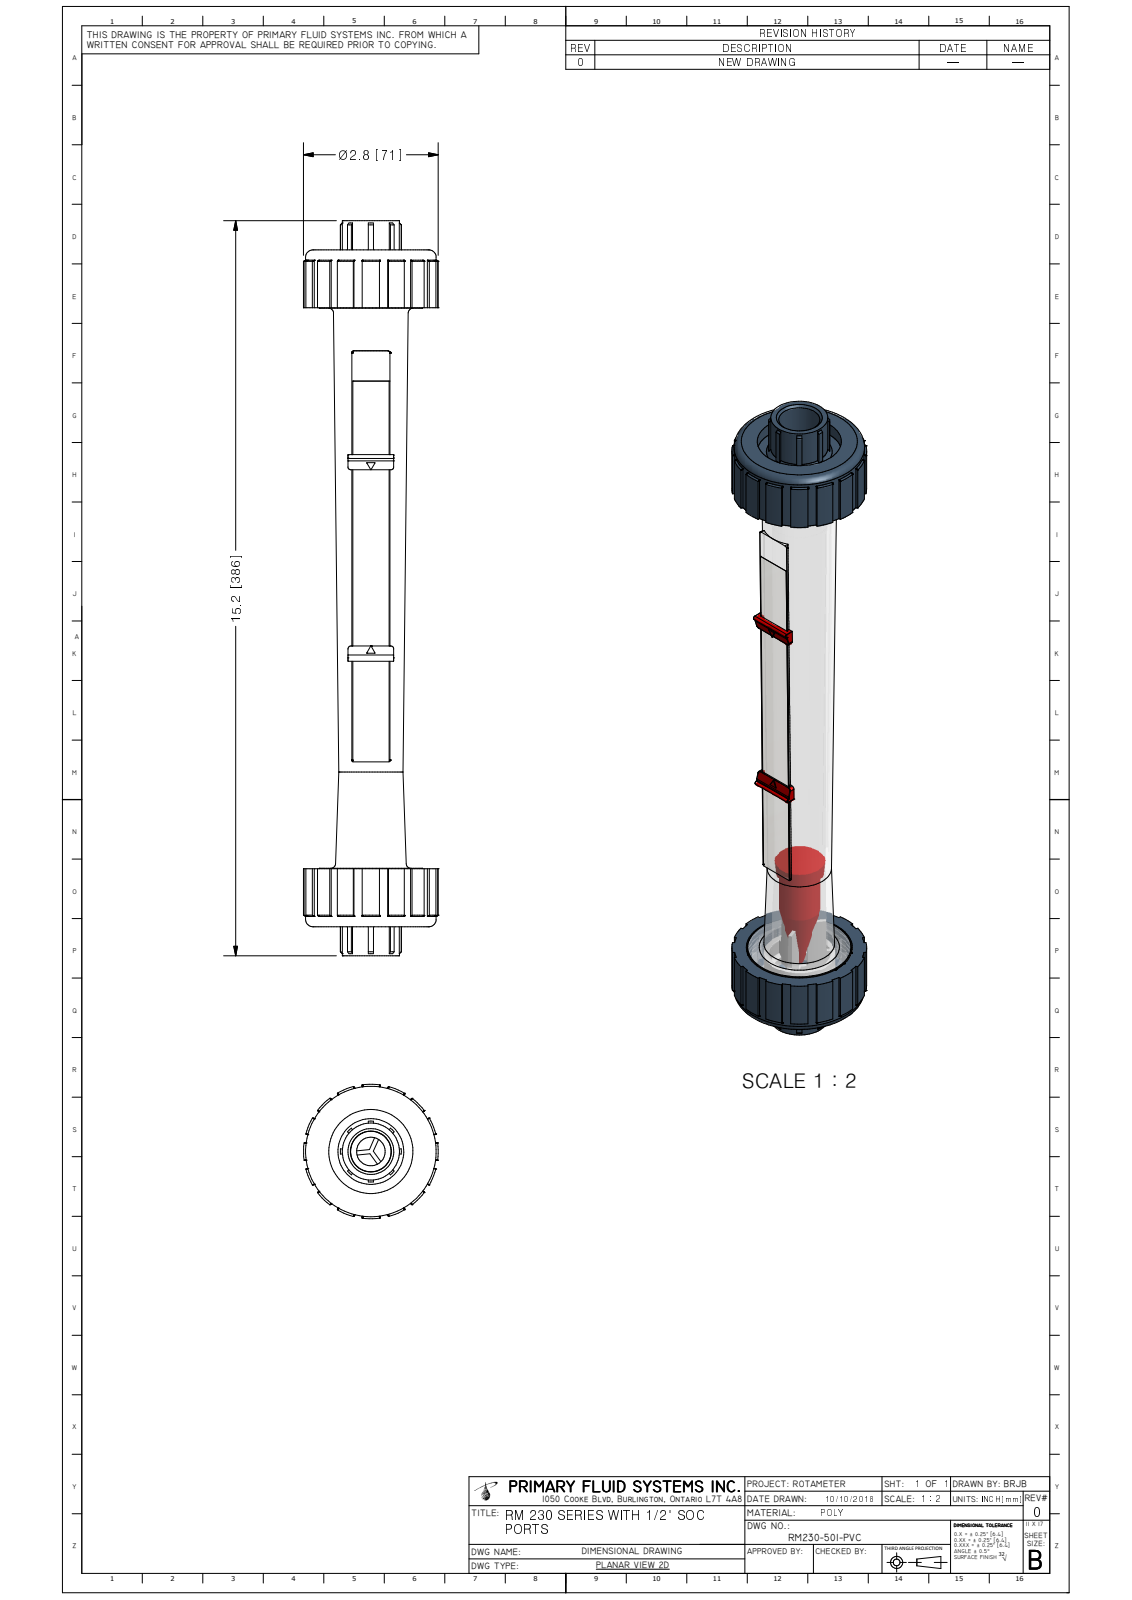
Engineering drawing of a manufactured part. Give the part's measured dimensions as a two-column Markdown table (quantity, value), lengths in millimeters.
| quantity | value |
| --- | --- |
| part name | RM230-50I-PVC_R0 |
| STEP written by | Autodesk Inventor 2009 (AUTOMOTIVE_DESIGN) |
| units | millimeters |
| bodies | 1 solid, 587 faces (230 planar, 140 cylindrical, 217 other) |
| overall size | 386.1 × 70.7 × 70.7 |
| volume | 526 000 mm³ |
| surface area | 107 100 mm² |
| round holes (diameter × count) | 44.1 × 1, 55.6 × 1 |
| round bosses / shafts (diameter × count) | 68.5 × 1, 54.7 × 1, 51.6 × 1, 37.7 × 1, 30 × 1 |
| partial cylindrical surfaces (radius × count) | 0.2 × 18, 0.3 × 16, 0.1 × 10, 0.2 × 4, 1.5 × 4, 0.2 × 2, 1 × 2, 1.1 × 2 |
| main face-to-face distances | 30.4, 325.1, 30.7, 324.8, 294.4, 12.6, 342.8, 17.8, 312.4, 6.5 |
